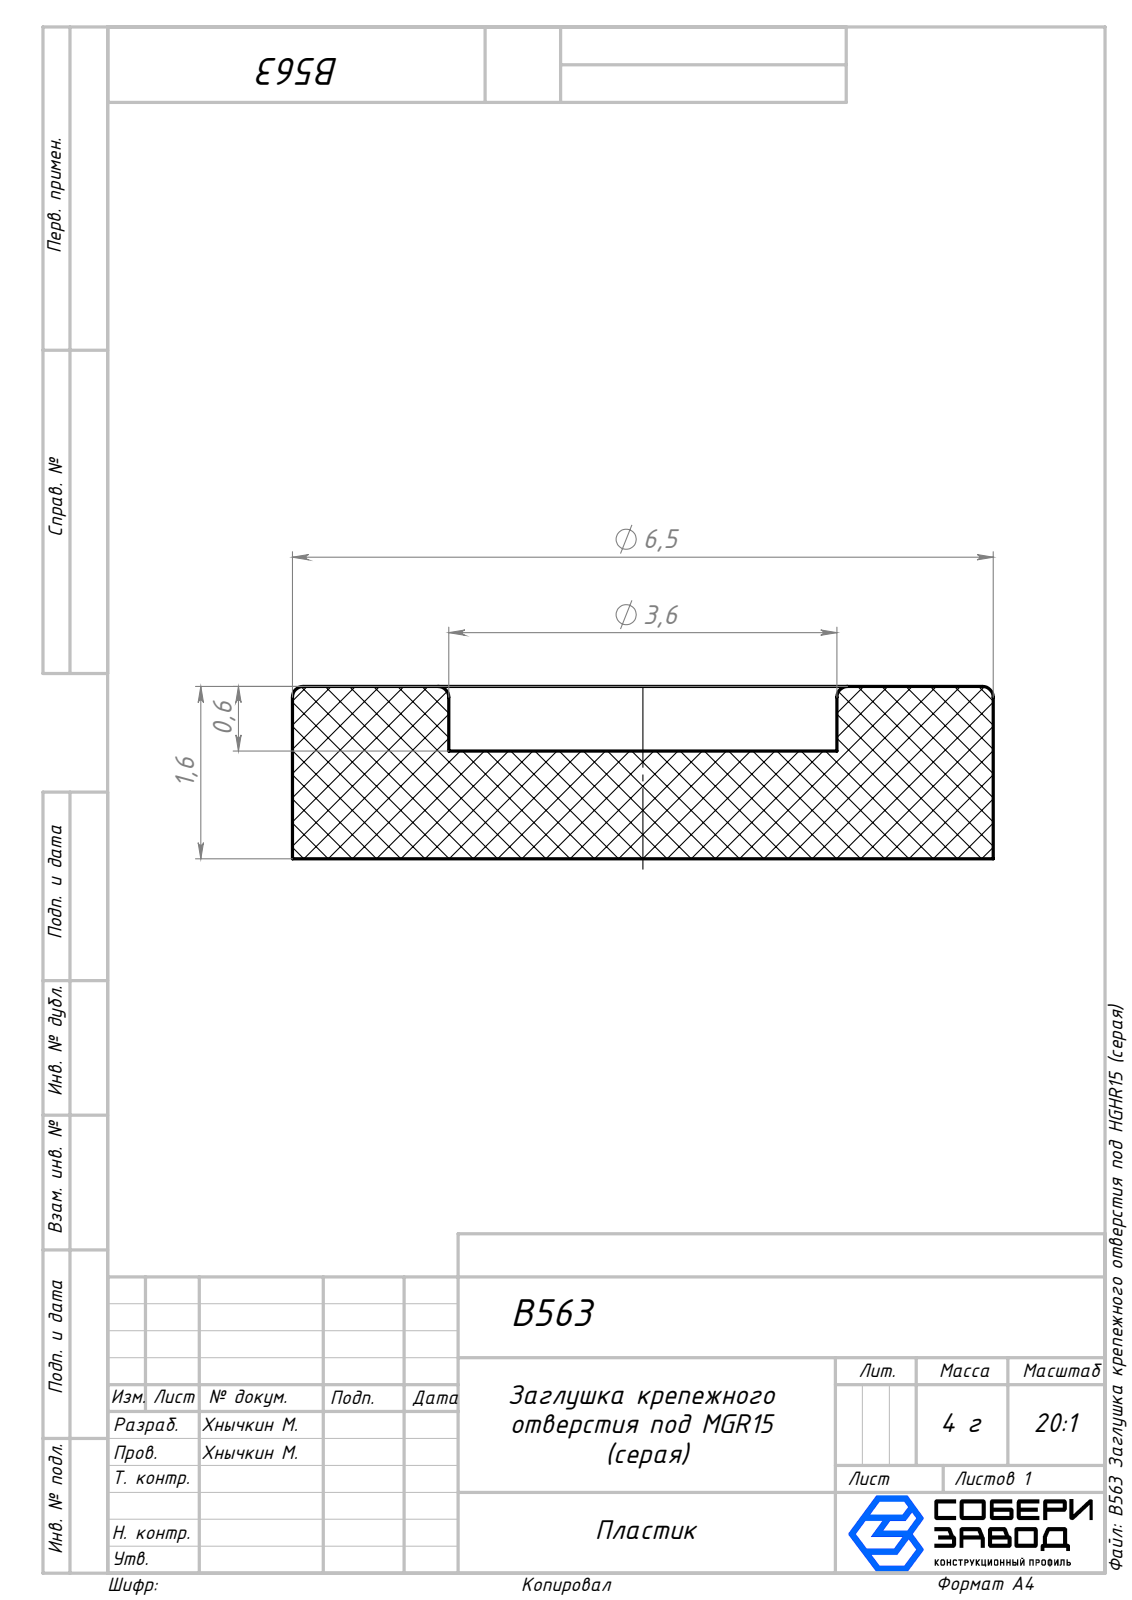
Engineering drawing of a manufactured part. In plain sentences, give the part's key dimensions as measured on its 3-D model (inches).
The part is named "B563 Заглушка крепежного отверстия под HGHR15 (серая)". Its 3-D file was written by "SolidWorks 2026 (AUTOMOTIVE_DESIGN)". It is 1 solid with 11 faces: 3 planar, 4 cylindrical and 4 other. Overall it measures 0.256 by 0.256 by 0.063 inches. Its volume is 0.003 cubic inches and its surface area 0.161 square inches. Round holes: 1 of diameter 0.142. Round bosses or shafts: 1 of diameter 0.256. The main face-to-face distances are 0.063, 0.039, 0.024.
